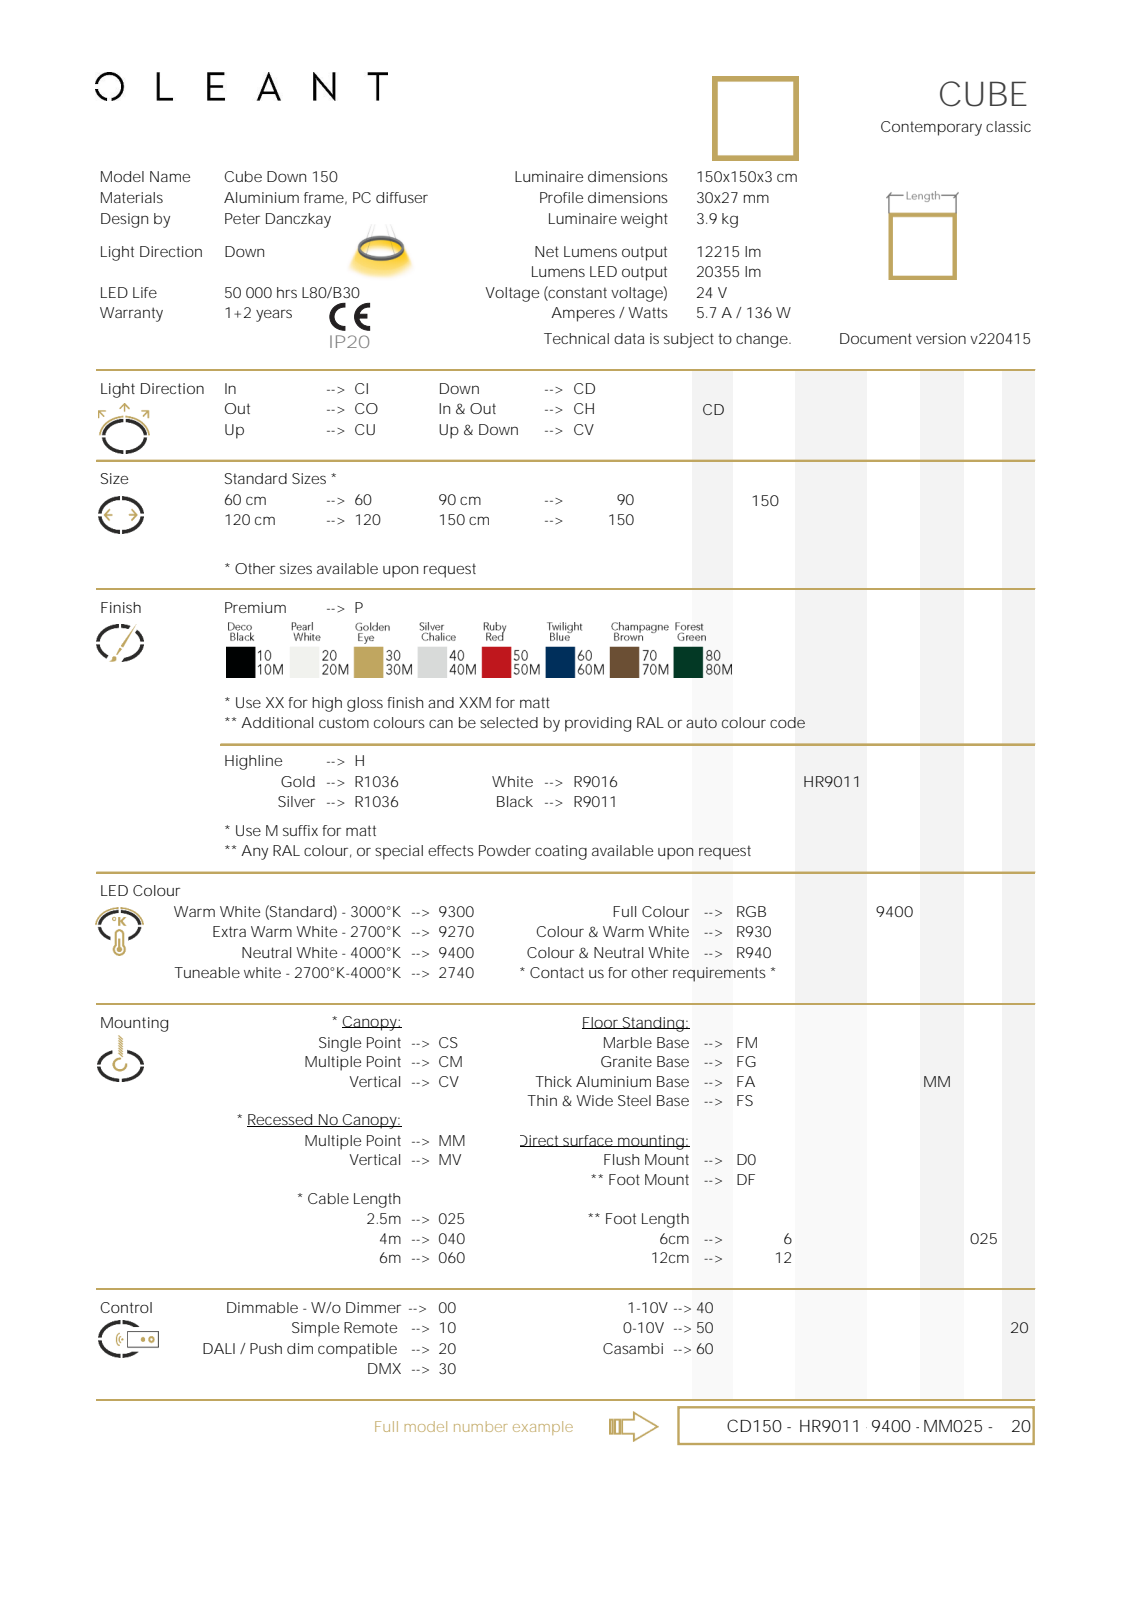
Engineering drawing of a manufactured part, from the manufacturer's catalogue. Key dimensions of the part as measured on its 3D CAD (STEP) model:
Part name (STEP PRODUCT): quad; frame; plexi; cable (+1 more)
STEP written by: Autodesk Inventor 2020 (AUTOMOTIVE_DESIGN)
Units: millimetres
Bodies: 10 solids, 180 faces (124 planar, 40 cylindrical, 16 other)
Overall size (bounding box): 1500 × 1500 × 1049.5
Volume: 4 522 000 mm³ · Surface area: 1 545 000 mm²
Round holes (diameter × count): ⌀3 ×4
Round bosses / shafts (diameter × count): ⌀11 ×4, ⌀9 ×4, ⌀4 ×4, ⌀1.2 ×4
Partial cylindrical surfaces — rounded edges, fillets, slot ends (radius × count): R0.75 ×20
Main face-to-face distances: 2, 1470, 28, 26, 24.5, 22.5, 1472, 1498, 30, 1468
Hole centre spacings: 1200, 1470, 1897.6
